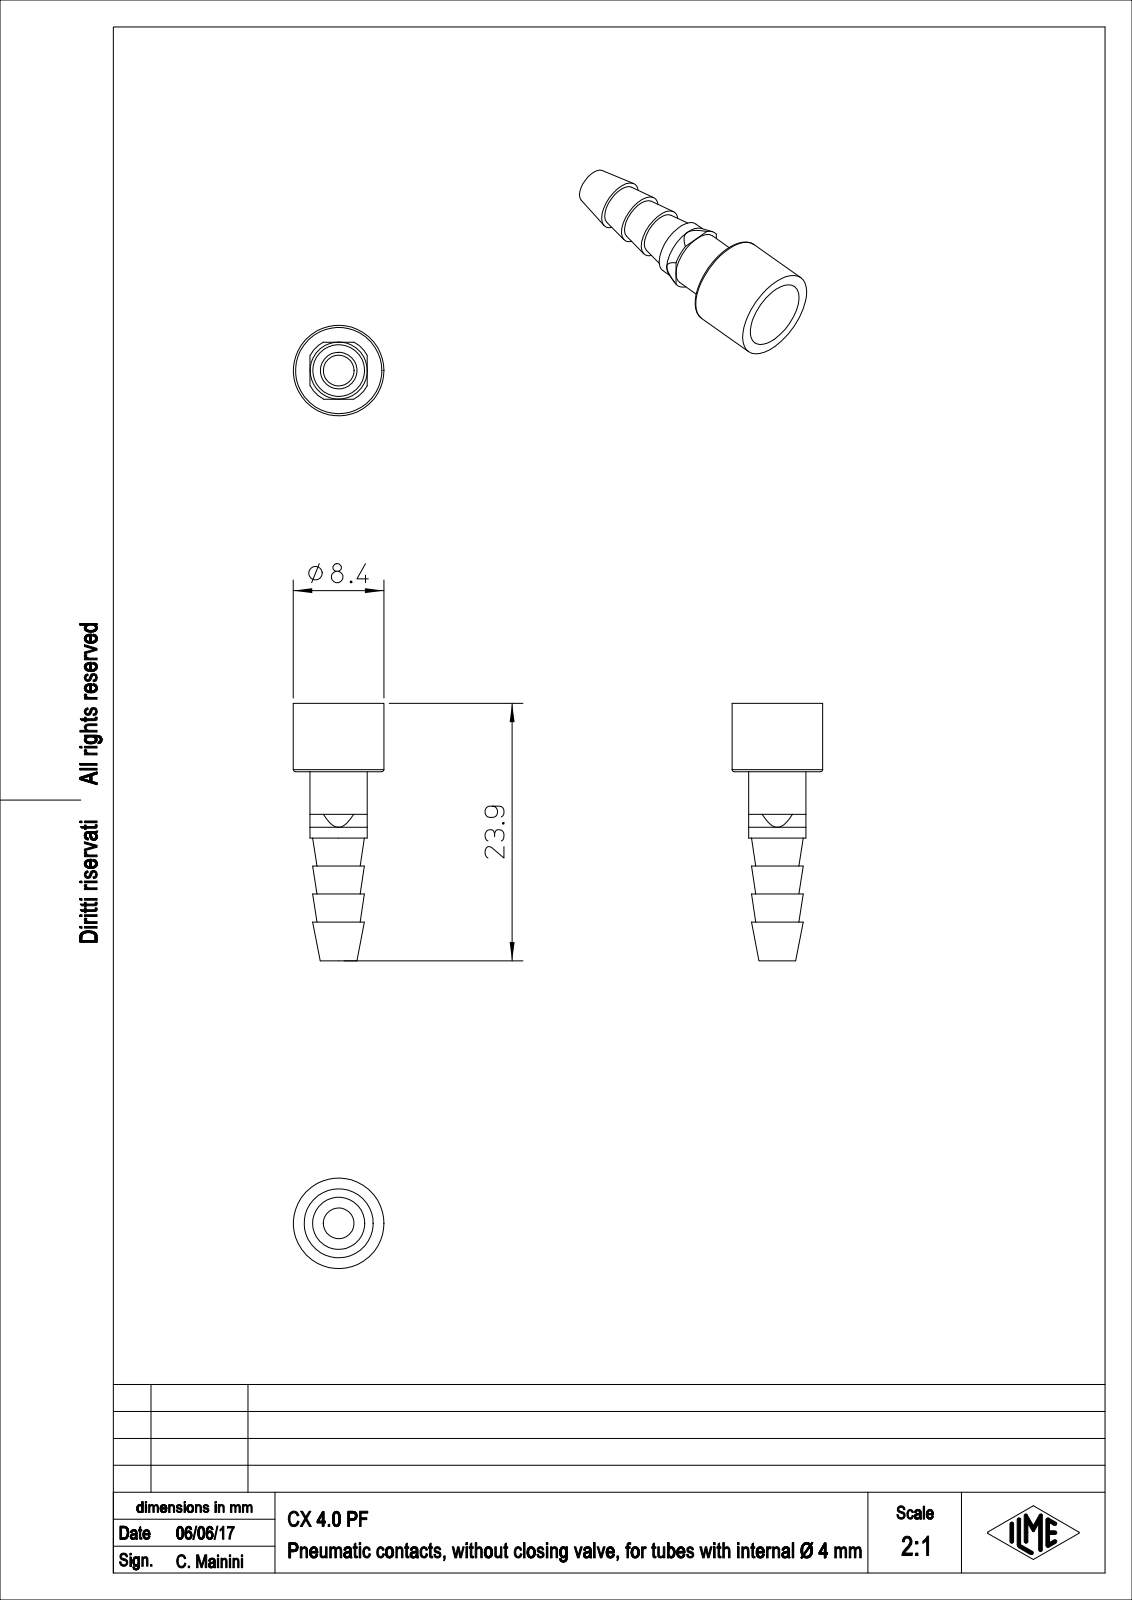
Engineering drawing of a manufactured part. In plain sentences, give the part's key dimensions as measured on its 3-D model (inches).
The part is named "CX_4.0_PF". Its 3-D file was written by "PTC Creo Elements/Direct Modeling 19.0E 27-Jun-2016 (C) Parametric Technology GmbH (AUTOMOTIVE_DESIGN)". It is 1 solid with 44 faces: 16 planar, 12 cylindrical and 16 other. Overall it measures 0.941 by 0.331 by 0.331 inches. Its volume is 0.018 cubic inches and its surface area 1.3 square inches. Round holes: 1 of diameter 0.112, 1 of diameter 0.191, 1 of diameter 0.252. Round bosses or shafts: 1 of diameter 0.331, 1 of diameter 0.209. The main face-to-face distances are 0.25, 0.209, 0.102, 0.041, 0.205, 0.549, 0.591, 0.799, 0.344, 0.386.
